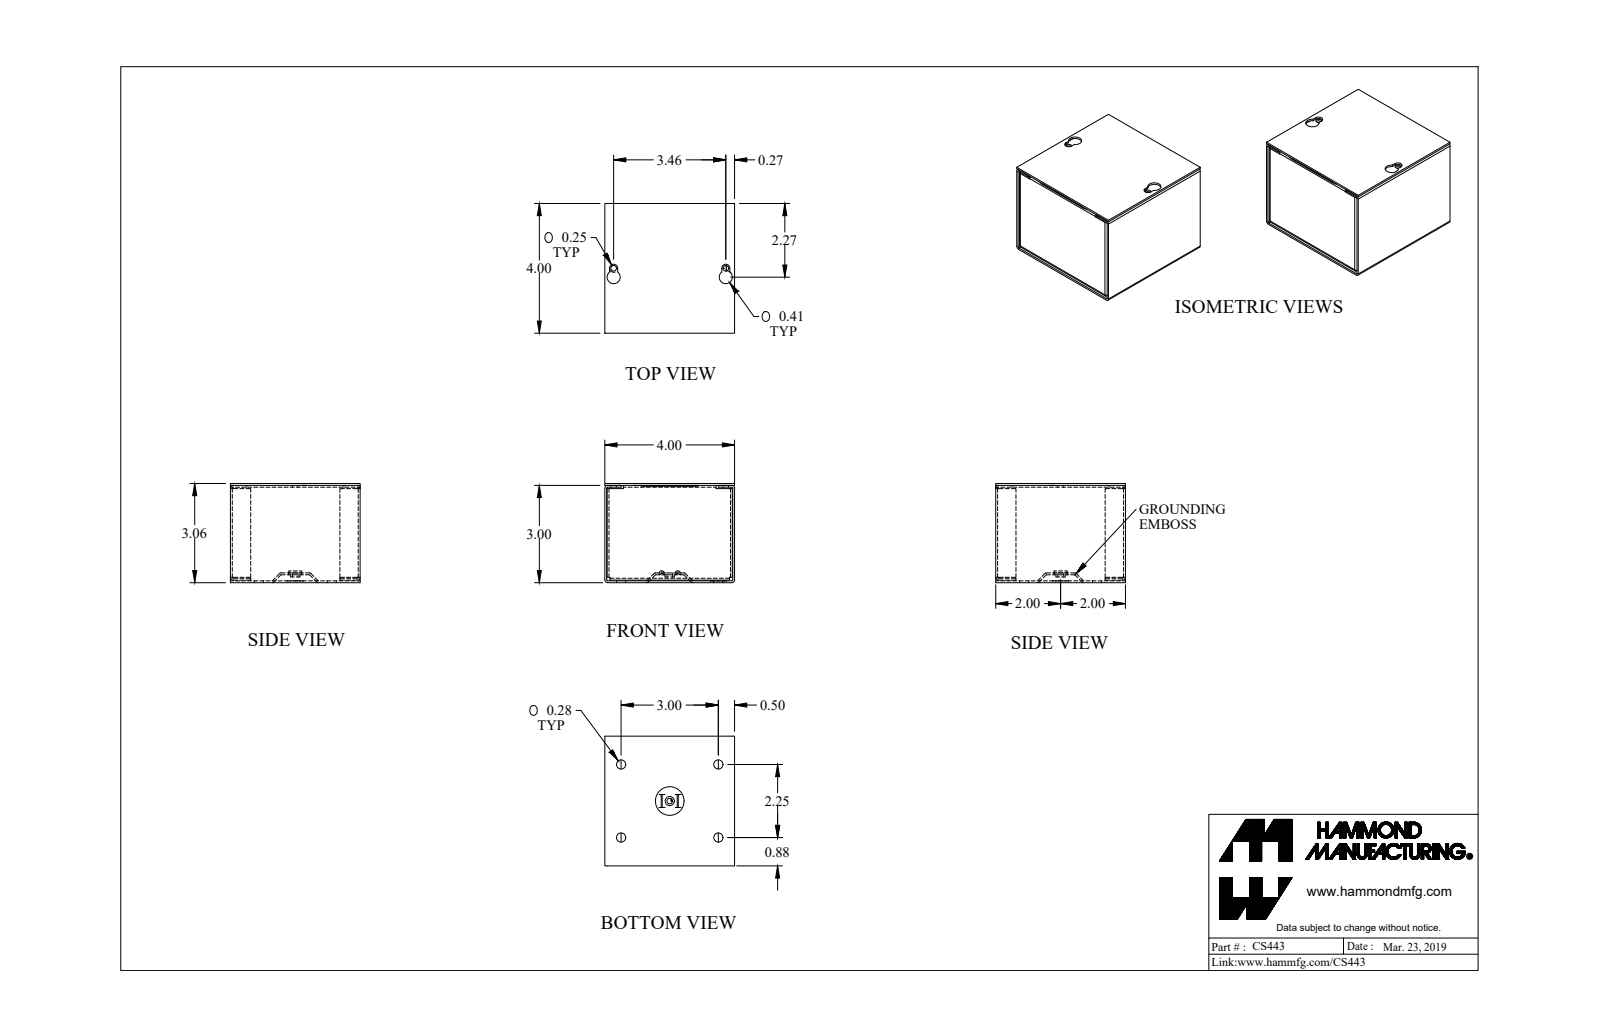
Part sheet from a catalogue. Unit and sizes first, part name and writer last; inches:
Units: inches
Overall size (bounding box): 4 × 4 × 3.057
Round holes (diameter × count): ⌀0.281 ×4, ⌀0.17 ×3, ⌀0.5 ×1
Round bosses / shafts (diameter × count): ⌀0.492 ×1, ⌀0.284 ×1
Partial cylindrical surfaces — rounded edges, fillets, slot ends (radius × count): R0.029 ×12, R0.086 ×12, R0.057 ×8, R0.125 ×2, R0.203 ×2
Main face-to-face distances: 0.057, 3.943, 3, 4, 3.886, 2.943, 3.057, 0.07, 3.873, 0.08
Hole centre spacings: 1.148, 1.875, 3.42, 1.125, 1.73, 2.25, 3, 3.204
Volume: 5.309 in³ · Surface area: 191.5 in²
Bodies: 4 solids, 189 faces (121 planar, 60 cylindrical, 8 other)
Part name (STEP PRODUCT): CS443_Default
STEP written by: SolidWorks 2019 (CONFIG_CONTROL_DESIGN)
